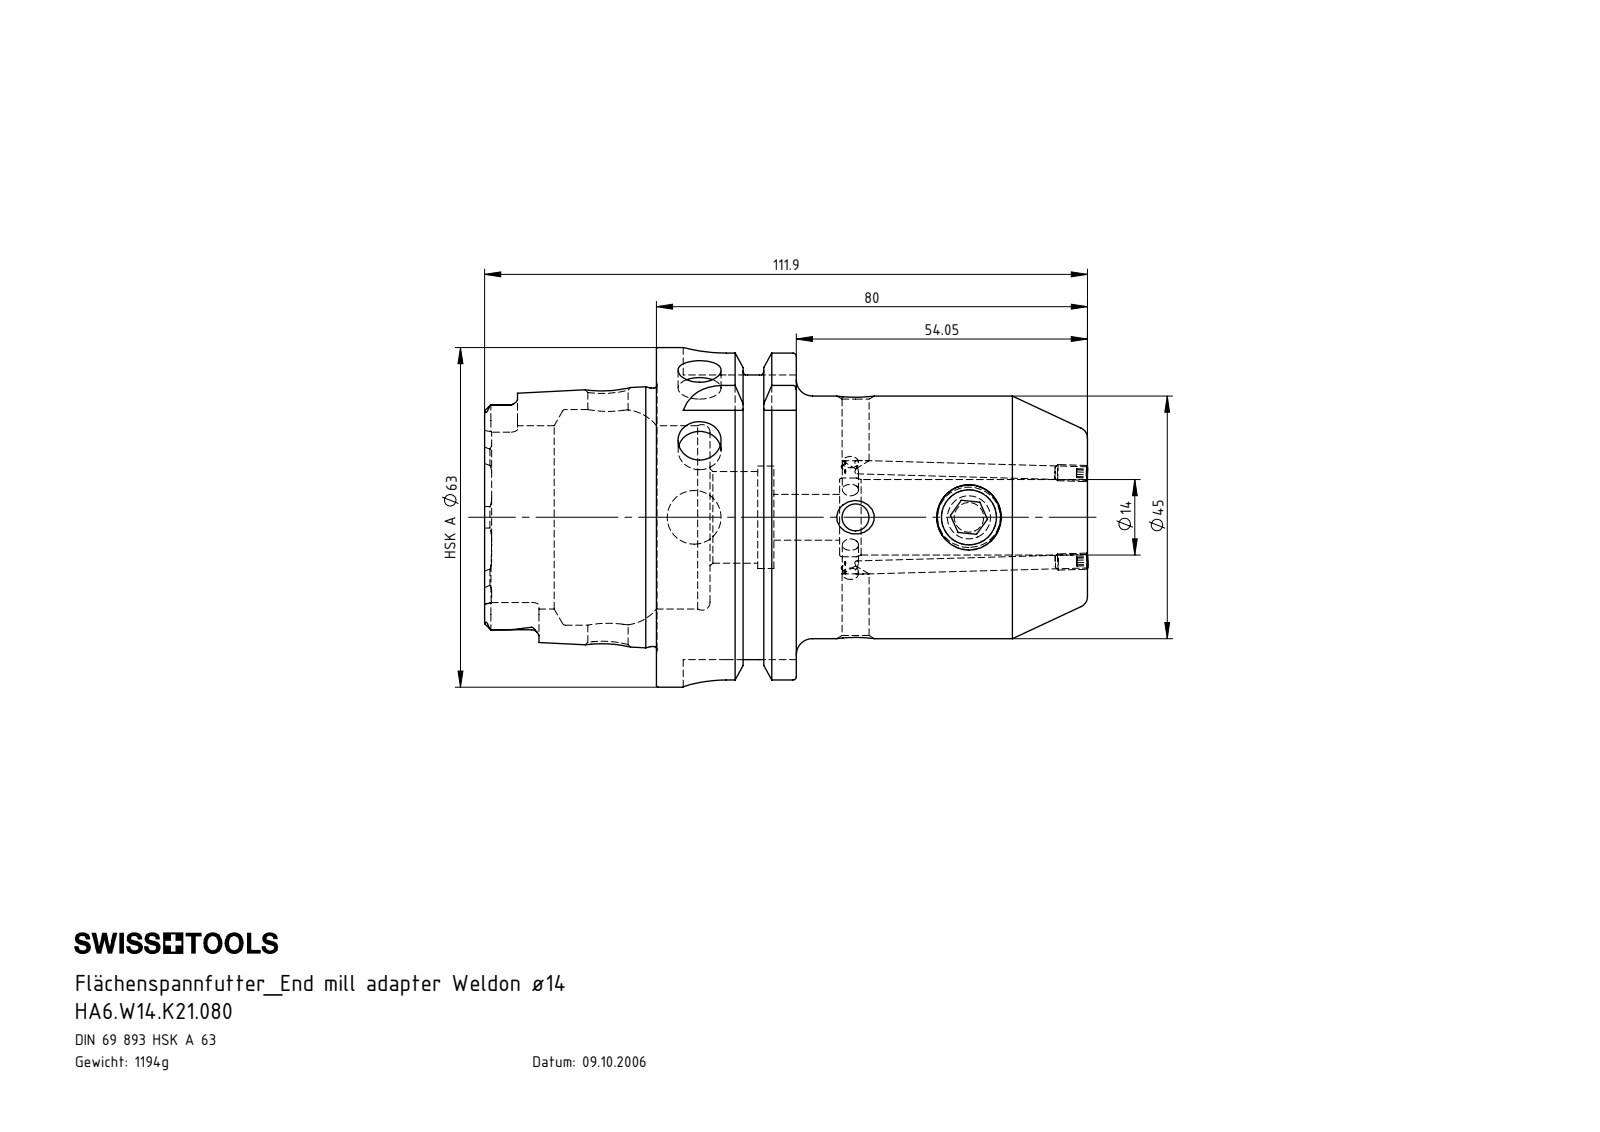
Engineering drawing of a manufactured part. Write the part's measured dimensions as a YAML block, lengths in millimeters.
part_name: "HA6.W14.K21.080; ERU-CJ2.001.006; W12-ER1.001.016; HA6-W14.K21.080_C_Fertigbearbeitung"
step_written_by: "SolidWorks 2012 (CONFIG_CONTROL_DESIGN)"
units: millimeters
bodies: {solids: 4, faces: 286, planar: 77, cylindrical: 81, other: 128}
overall_size: [111.98, 63, 63]
volume: 152155
surface_area: 34218
round_holes:
  - {diameter: 2.5, count: 2}
  - {diameter: 5, count: 2}
  - {diameter: 8, count: 2}
  - {diameter: 3, count: 1}
  - {diameter: 7.5, count: 1}
  - {diameter: 8.5, count: 1}
  - {diameter: 10, count: 1}
  - {diameter: 10.25, count: 1}
  - {diameter: 14, count: 1}
  - {diameter: 14.6, count: 1}
  - {diameter: 17, count: 1}
  - {diameter: 19, count: 1}
round_bosses_or_shafts:
  - {diameter: 3, count: 2}
  - {diameter: 63, count: 1}
  - {diameter: 54.95, count: 1}
  - {diameter: 47.94, count: 1}
  - {diameter: 45, count: 1}
  - {diameter: 12, count: 1}
partial_cylinders:
  - {radius: 1.4, count: 6}
  - {radius: 2.88, count: 4}
  - {radius: 8, count: 4}
face_to_face_distances: [25.95, 16, 9.95, 80, 70.05, 54.05, 31.9, 41.85, 57.85, 111.9]
hole_center_spacings: [21.05, 29.95, 45.95, 51]
